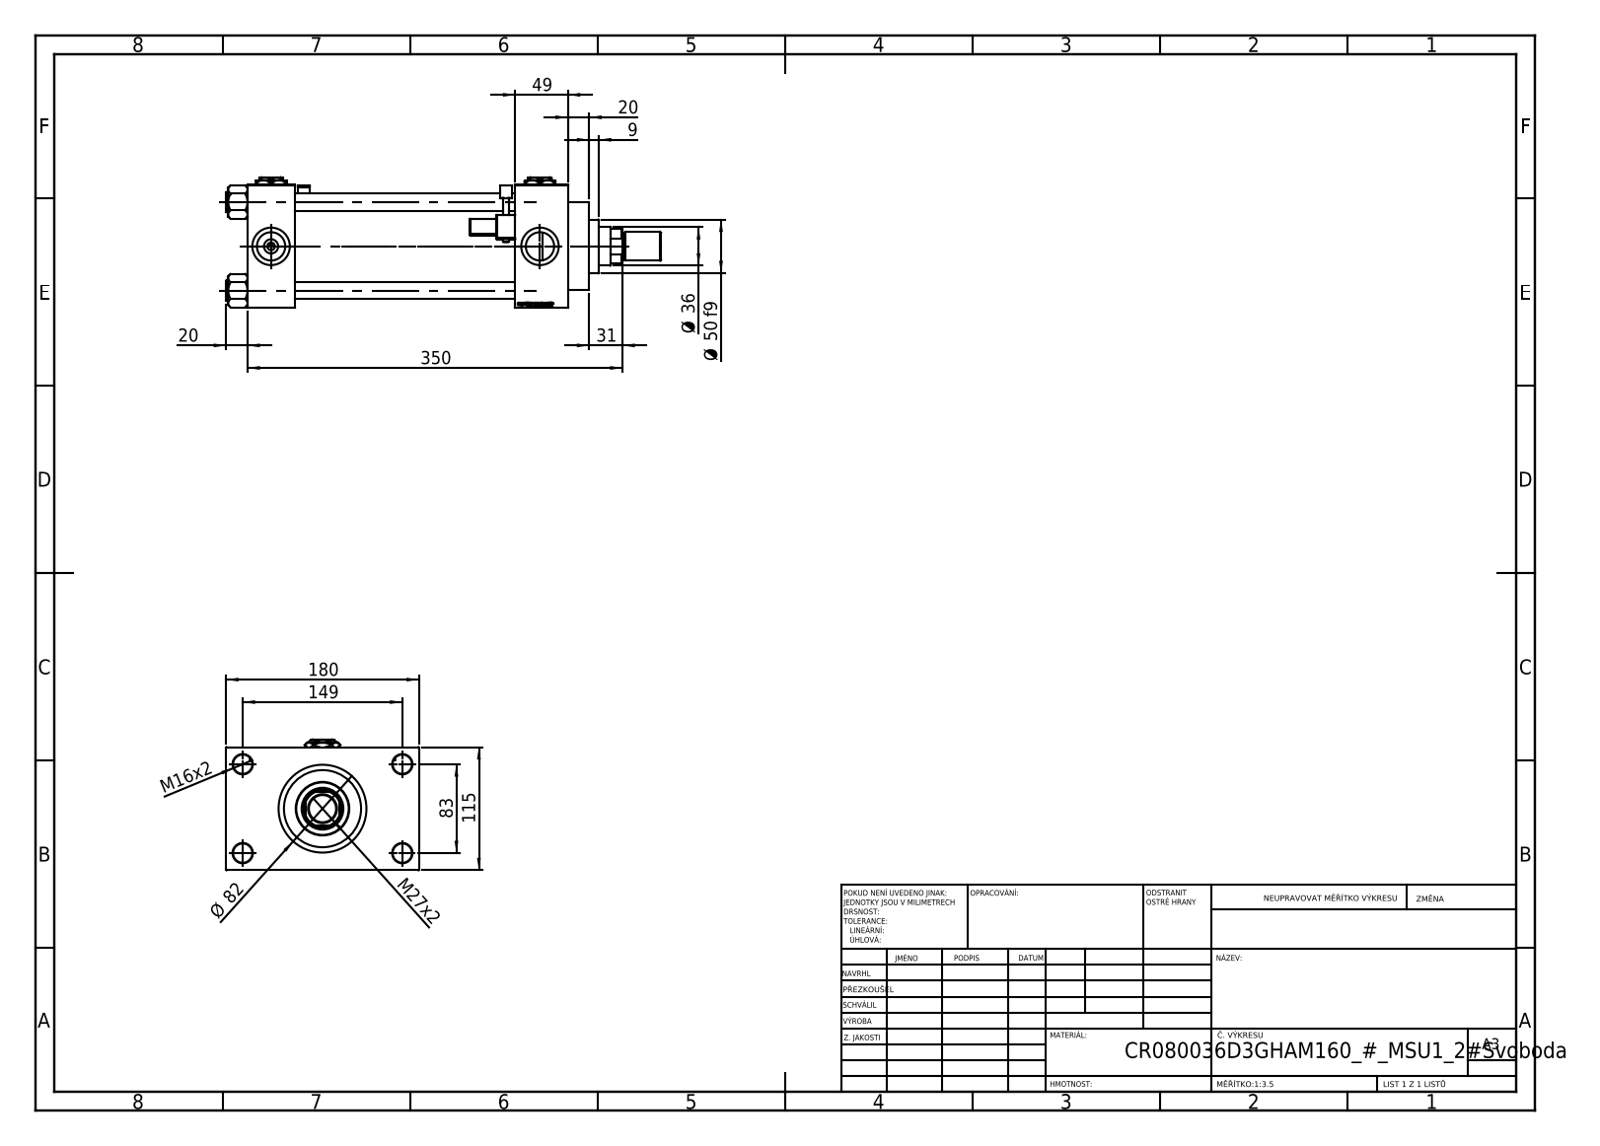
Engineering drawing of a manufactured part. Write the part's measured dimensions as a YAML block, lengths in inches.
part_name: "V215CR_VCP_D; V215CR_MSU; V215CR_D_TYCINKA; V215_VC_A (+4 more)"
step_written_by: "SolidWorks 2019 (CONFIG_CONTROL_DESIGN)"
units: inches
bodies: {solids: 16, faces: 1420, planar: 655, cylindrical: 163, other: 602}
overall_size: [15.984, 7.087, 4.803]
volume: 146
surface_area: 677.4
round_holes:
  - {diameter: 0.63, count: 4}
  - {diameter: 0.709, count: 4}
  - {diameter: 1.041, count: 4}
  - {diameter: 1.378, count: 4}
  - {diameter: 0.276, count: 3}
  - {diameter: 1.004, count: 1}
  - {diameter: 1.417, count: 1}
  - {diameter: 1.535, count: 1}
  - {diameter: 2.402, count: 1}
  - {diameter: 2.835, count: 1}
  - {diameter: 3.15, count: 1}
round_bosses_or_shafts:
  - {diameter: 0.748, count: 4}
  - {diameter: 0.236, count: 2}
  - {diameter: 3.386, count: 1}
  - {diameter: 3.228, count: 1}
  - {diameter: 1.969, count: 1}
  - {diameter: 1.063, count: 1}
  - {diameter: 0.984, count: 1}
partial_cylinders:
  - {radius: 0.02, count: 48}
  - {radius: 0.039, count: 2}
  - {radius: 0.098, count: 2}
  - {radius: 0.157, count: 2}
  - {radius: 0.689, count: 1}
face_to_face_distances: [4.528, 8.11, 10.039, 1.929, 1.732, 9.843, 11.772, 1.28, 5.807, 7.087]
hole_center_spacings: [1.305, 2.302, 3.256, 3.357, 3.513, 4.561, 5.607, 3.268]
